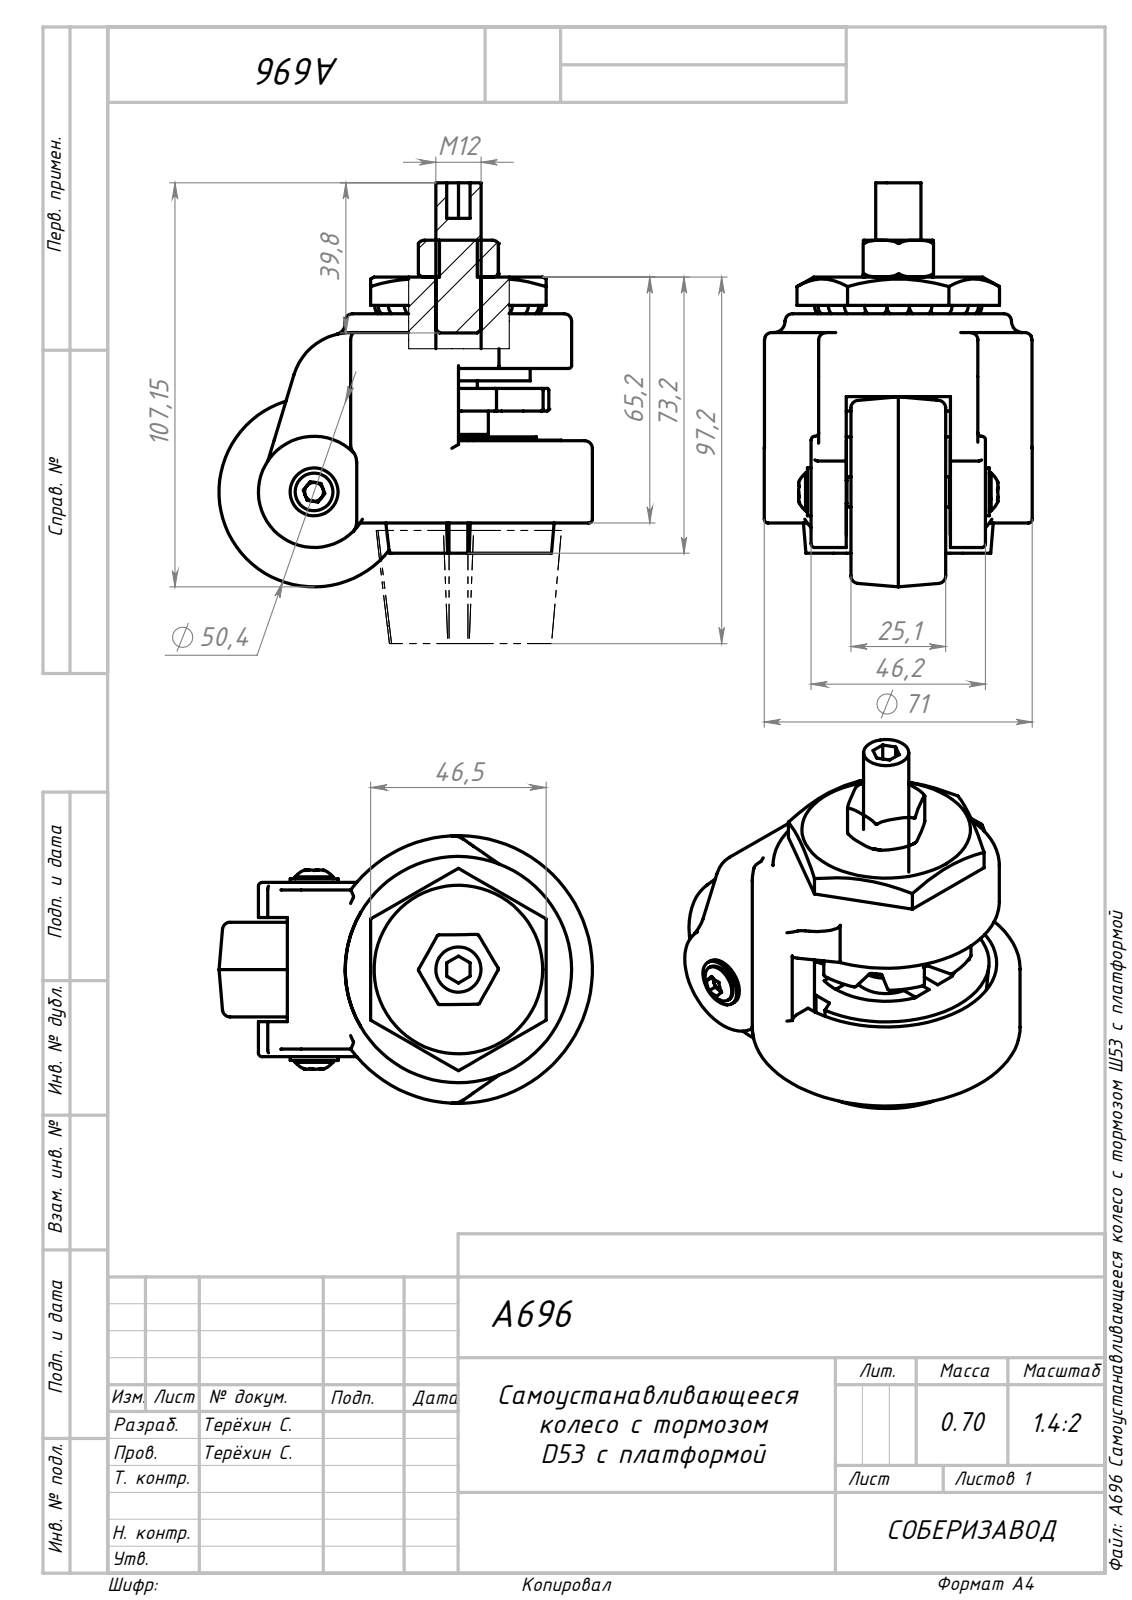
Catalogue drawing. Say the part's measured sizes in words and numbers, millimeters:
The part is named "A696 Втулка_00; A696 Регулировка опоры_00; A696 Крепление ножки_00; A696 Самоустанавливающееся колесо с тормозом Ø53 с платформой_2 (+8 more)". Its 3-D file was written by "SolidWorks 2022 (AUTOMOTIVE_DESIGN)". It is 35 solids with 865 faces: 236 planar, 307 cylindrical and 322 other. Overall it measures 107.15 by 98.95 by 71 millimeters. Its volume is 221 373 cubic millimeters and its surface area 75 481 square millimeters. Round holes: 1 of diameter 6, 1 of diameter 10.2, 1 of diameter 11, 1 of diameter 12, 1 of diameter 28.2, 1 of diameter 38, 1 of diameter 40, 1 of diameter 58.6. Round bosses or shafts: 2 of diameter 10, 1 of diameter 71, 1 of diameter 20, 1 of diameter 12.7, 1 of diameter 8. Partial cylindrical surfaces (rounded edges, fillets, slot ends): 124 of radius 0.5, 20 of radius 2, 6 of radius 5, 4 of radius 1, 2 of radius 0.75, 1 of radius 8.4, 1 of radius 9.68, 1 of radius 14.2. The main face-to-face distances are 26.35, 8, 1.25, 2, 24.2, 29.7, 0.84, 73.2, 5.3, 49.
